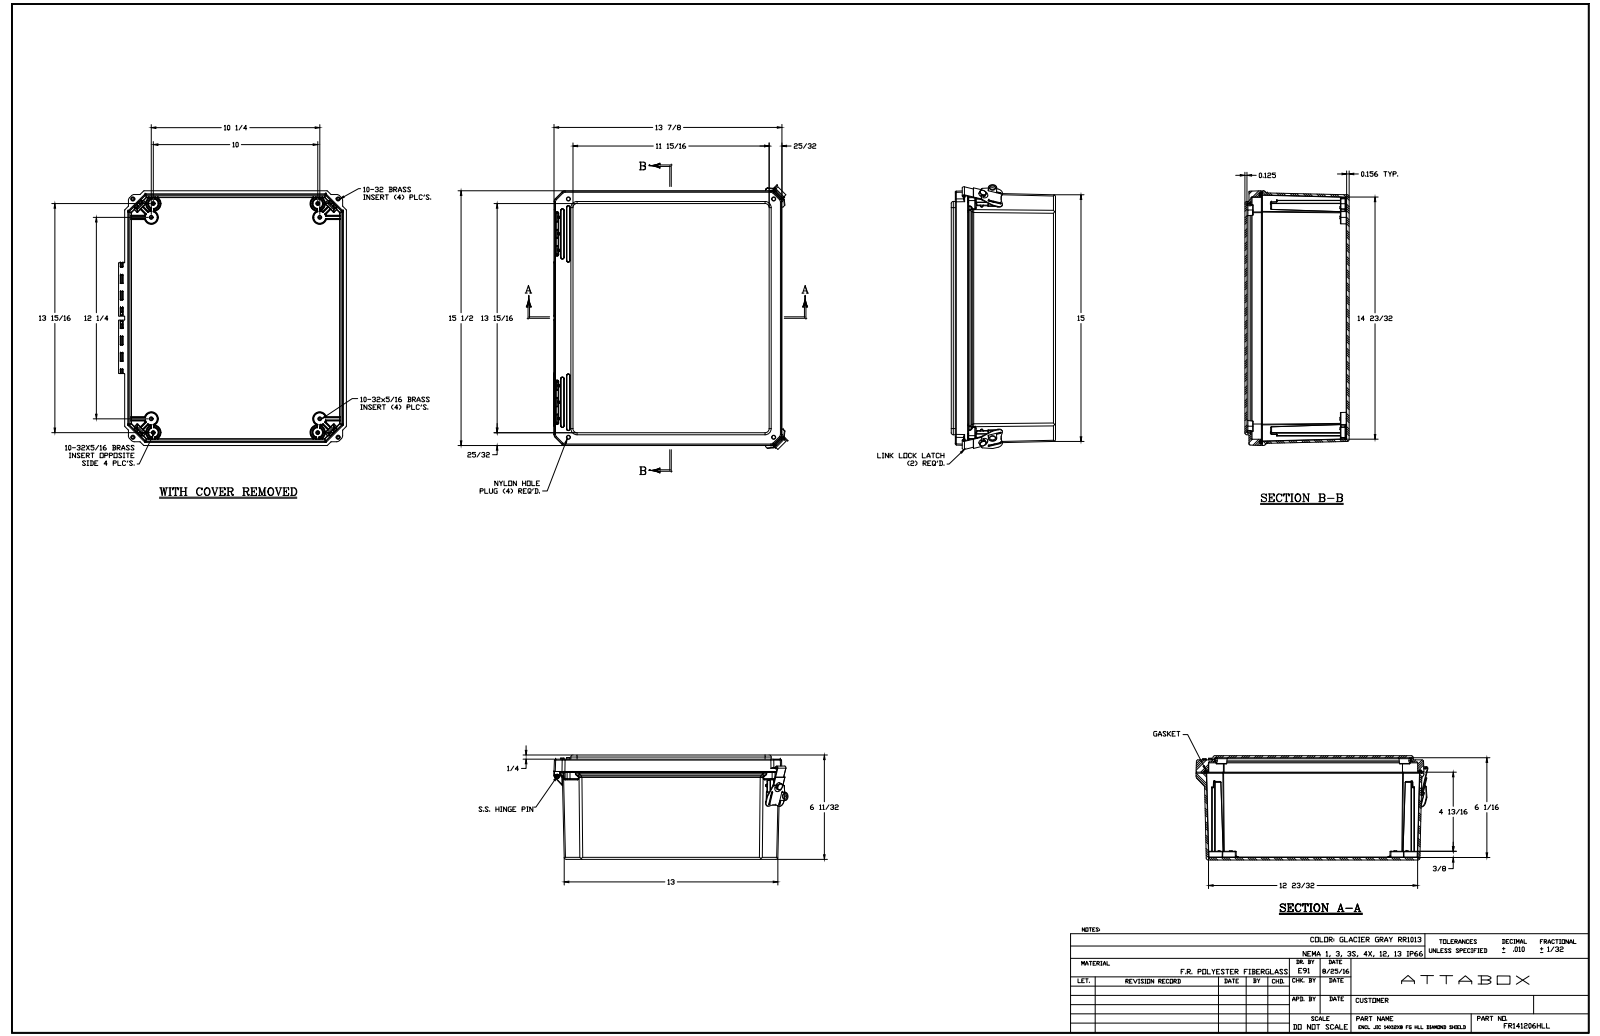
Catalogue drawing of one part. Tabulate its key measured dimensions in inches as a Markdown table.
| quantity | value |
| --- | --- |
| part name | FR141206HLL |
| STEP written by | SolidWorks 2018 (AUTOMOTIVE_DESIGN) |
| units | inches |
| bodies | 37 solids, 2343 faces (803 planar, 924 cylindrical, 616 other) |
| overall size | 16.348 × 14.298 × 6.344 |
| volume | 121 in³ |
| surface area | 1 637 in² |
| round holes (diameter × count) | 0.156 × 16, 0.152 × 8, 0.098 × 4, 0.15 × 4, 0.252 × 4, 0.253 × 4, 0.05 × 2, 0.12 × 2, 0.137 × 2, 0.219 × 2, 0.227 × 2, 0.313 × 2 |
| round bosses / shafts (diameter × count) | 0.246 × 16, 0.87 × 4, 0.209 × 4, 0.2 × 4, 0.135 × 4, 0.6 × 2, 0.435 × 2, 0.05 × 2 |
| partial cylindrical surfaces (radius × count) | 0.01 × 198, 0.005 × 96, 0.02 × 49, 0.03 × 45, 0.125 × 34, 0.039 × 28, 0.03 × 24, 0.063 × 24 |
| main face-to-face distances | 0.156, 0.125, 6.187, 6.343, 6.219, 6.063, 0.14, 0.139, 0.25, 0.125 |
| hole center spacings | 1.582, 10.16, 13.416, 0.429, 0.793, 0.84, 1.277, 10.252 |
